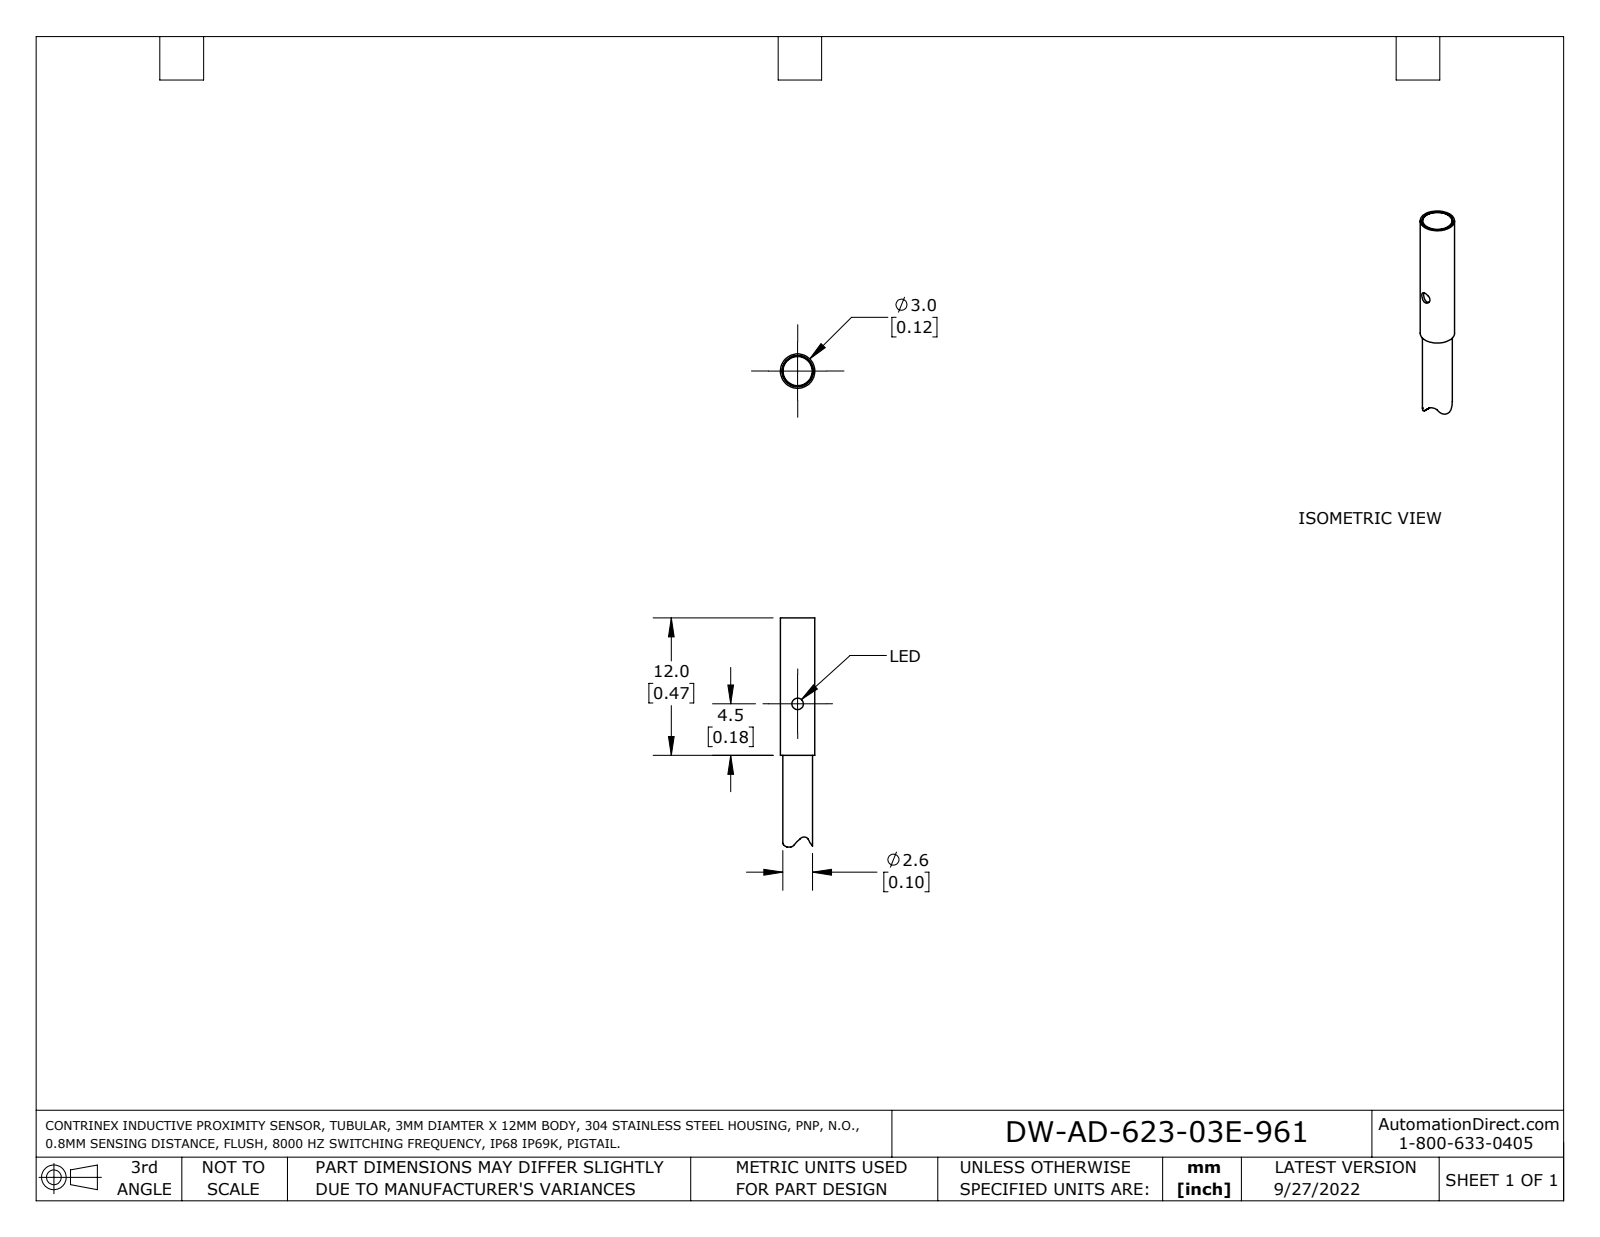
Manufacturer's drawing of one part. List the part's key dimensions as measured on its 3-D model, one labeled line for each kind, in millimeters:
Part name (STEP PRODUCT): DW-AD-623-03E-961
STEP written by: SolidWorks 2021 (AUTOMOTIVE_DESIGN)
Units: millimetres
Bodies: 1 solid, 21 faces (6 planar, 13 cylindrical, 2 other)
Overall size (bounding box): 20 × 3 × 3
Volume: 100 mm³ · Surface area: 210 mm²
Round holes (diameter × count): ⌀1 ×1, ⌀2.7 ×1
Round bosses / shafts (diameter × count): ⌀3 ×1, ⌀2.6 ×1, ⌀2.6 ×1
Partial cylindrical surfaces — rounded edges, fillets, slot ends (radius × count): R0.4 ×1, R0.6 ×1, R2.4 ×1, R3.6 ×1, R4.8 ×1
Main face-to-face distances: 12, 20, 8, 11, 1, 9, 10.9, 11.9, 19.9
